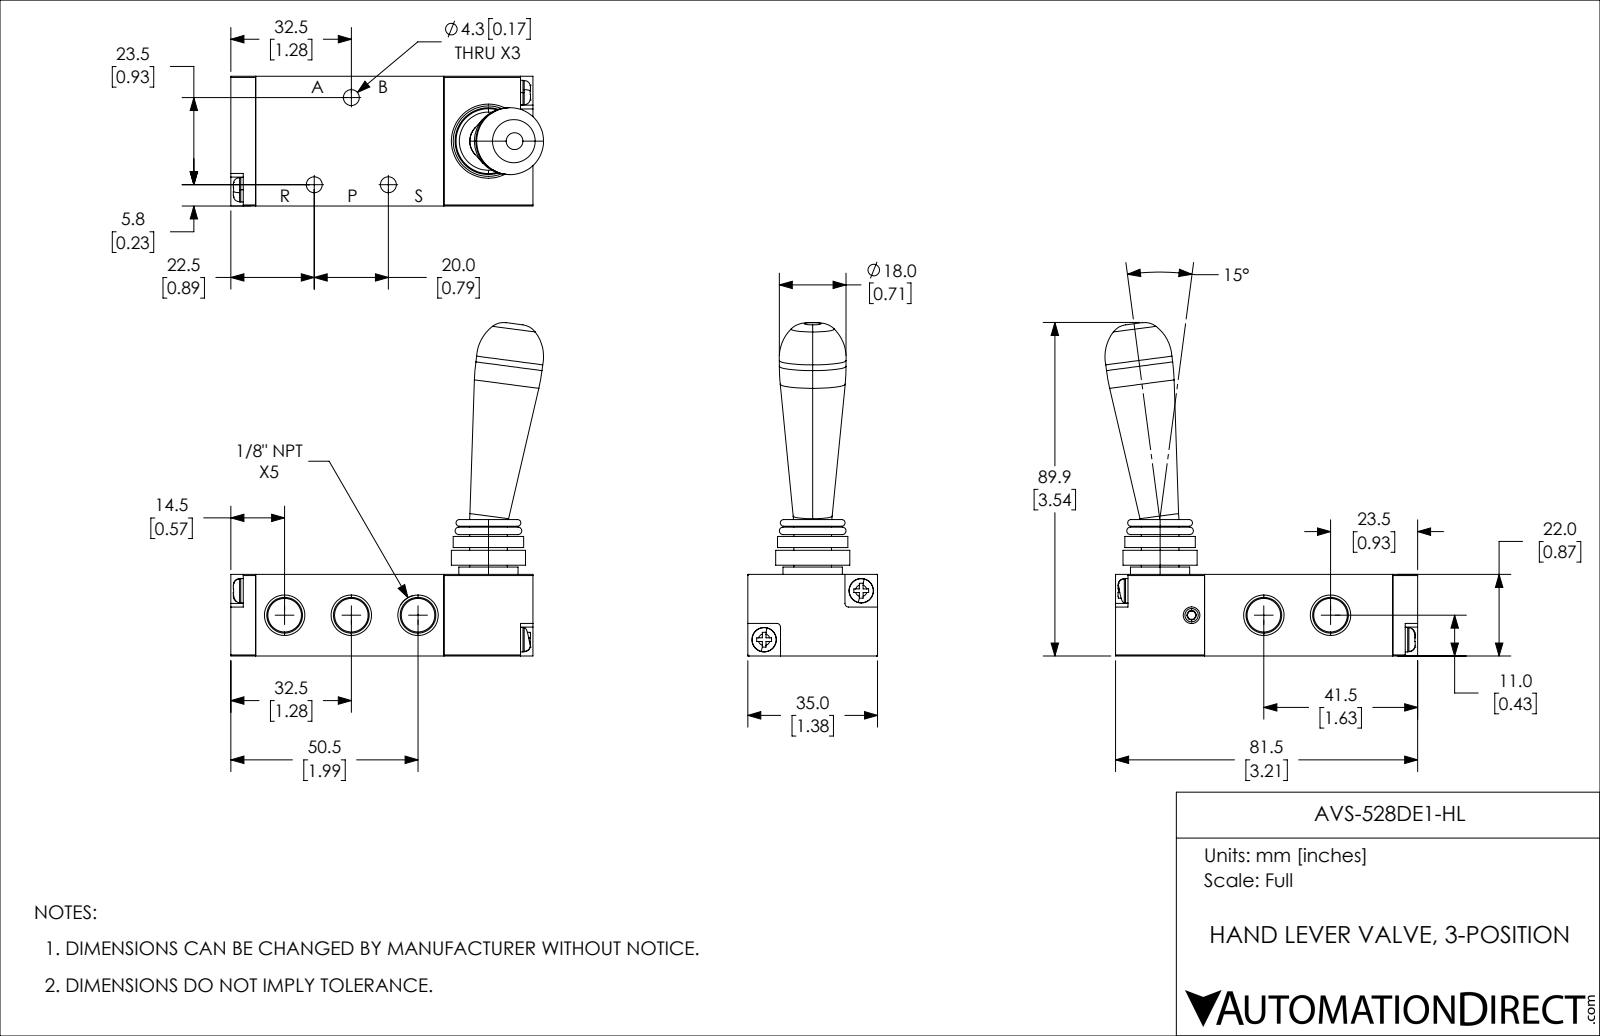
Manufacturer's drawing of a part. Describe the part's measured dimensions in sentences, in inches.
The part is named "AVS-528DE1-HL". Its 3-D file was written by "SolidWorks 2018 (AUTOMOTIVE_DESIGN)". It is 4 solids with 228 faces: 128 planar, 56 cylindrical and 44 other. Overall it measures 3.541 by 3.322 by 1.378 inches. Its volume is 4.272 cubic inches and its surface area 33.78 square inches. Round holes: 3 of diameter 0.169, 1 of diameter 0.177, 1 of diameter 0.63. Round bosses or shafts: 4 of diameter 0.26, 4 of diameter 0.256, 1 of diameter 0.787, 1 of diameter 0.748, 1 of diameter 0.709, 1 of diameter 0.4, 1 of diameter 0.142. Partial cylindrical surfaces (rounded edges, fillets, slot ends): 4 of radius 0.012, 4 of radius 0.039. The main face-to-face distances are 0.866, 1.378, 2, 0.945, 2.945, 0.079, 0.264, 3.209, 2.264, 0.157. The hole center spacings are 1.006, 0.787, 1.159, 1.528, 1.907.
